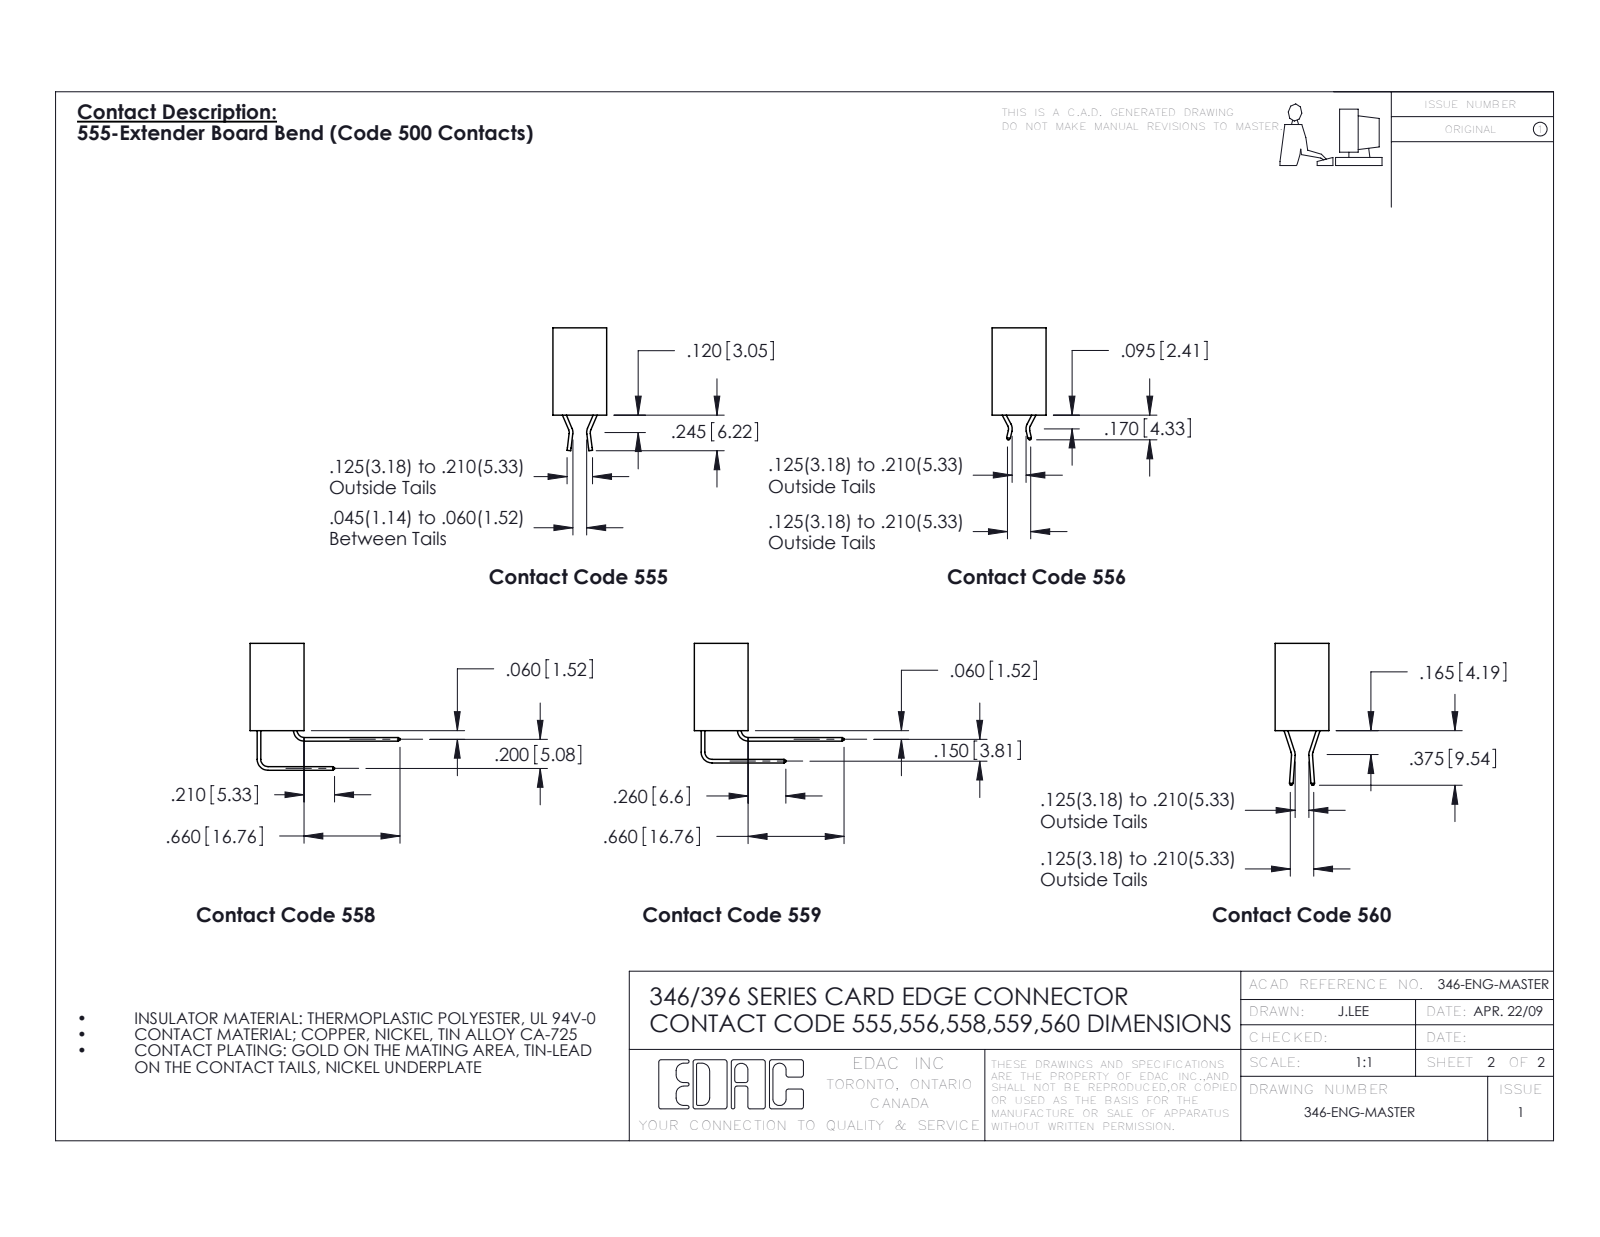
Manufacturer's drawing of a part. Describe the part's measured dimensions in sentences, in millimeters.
The part is named "346 Part_No Mounting Lugs; 396-015-559-101; 345-292-001_558 559 Tail - 1". Its 3-D file was written by "SolidWorks 2016 (CONFIG_CONTROL_DESIGN)". It is 16 solids with 1014 faces: 702 planar, 312 cylindrical and 0 other. Overall it measures 54.9 by 26.2 by 17.1 millimeters. Its volume is 5 670 cubic millimeters and its surface area 7 161 square millimeters. Round holes: 1 of diameter 1.6. Partial cylindrical surfaces (rounded edges, fillets, slot ends): 30 of radius 0.2, 22 of radius 0.3, 6 of radius 0.2, 6 of radius 0.8, 3 of radius 0.7, 2 of radius 0.8, 2 of radius 1, 1 of radius 0.4. The main face-to-face distances are 1.2, 6.4, 8.2, 9.4, 0.6, 1.8, 3.8, 5.6, 2.5, 4.4.
